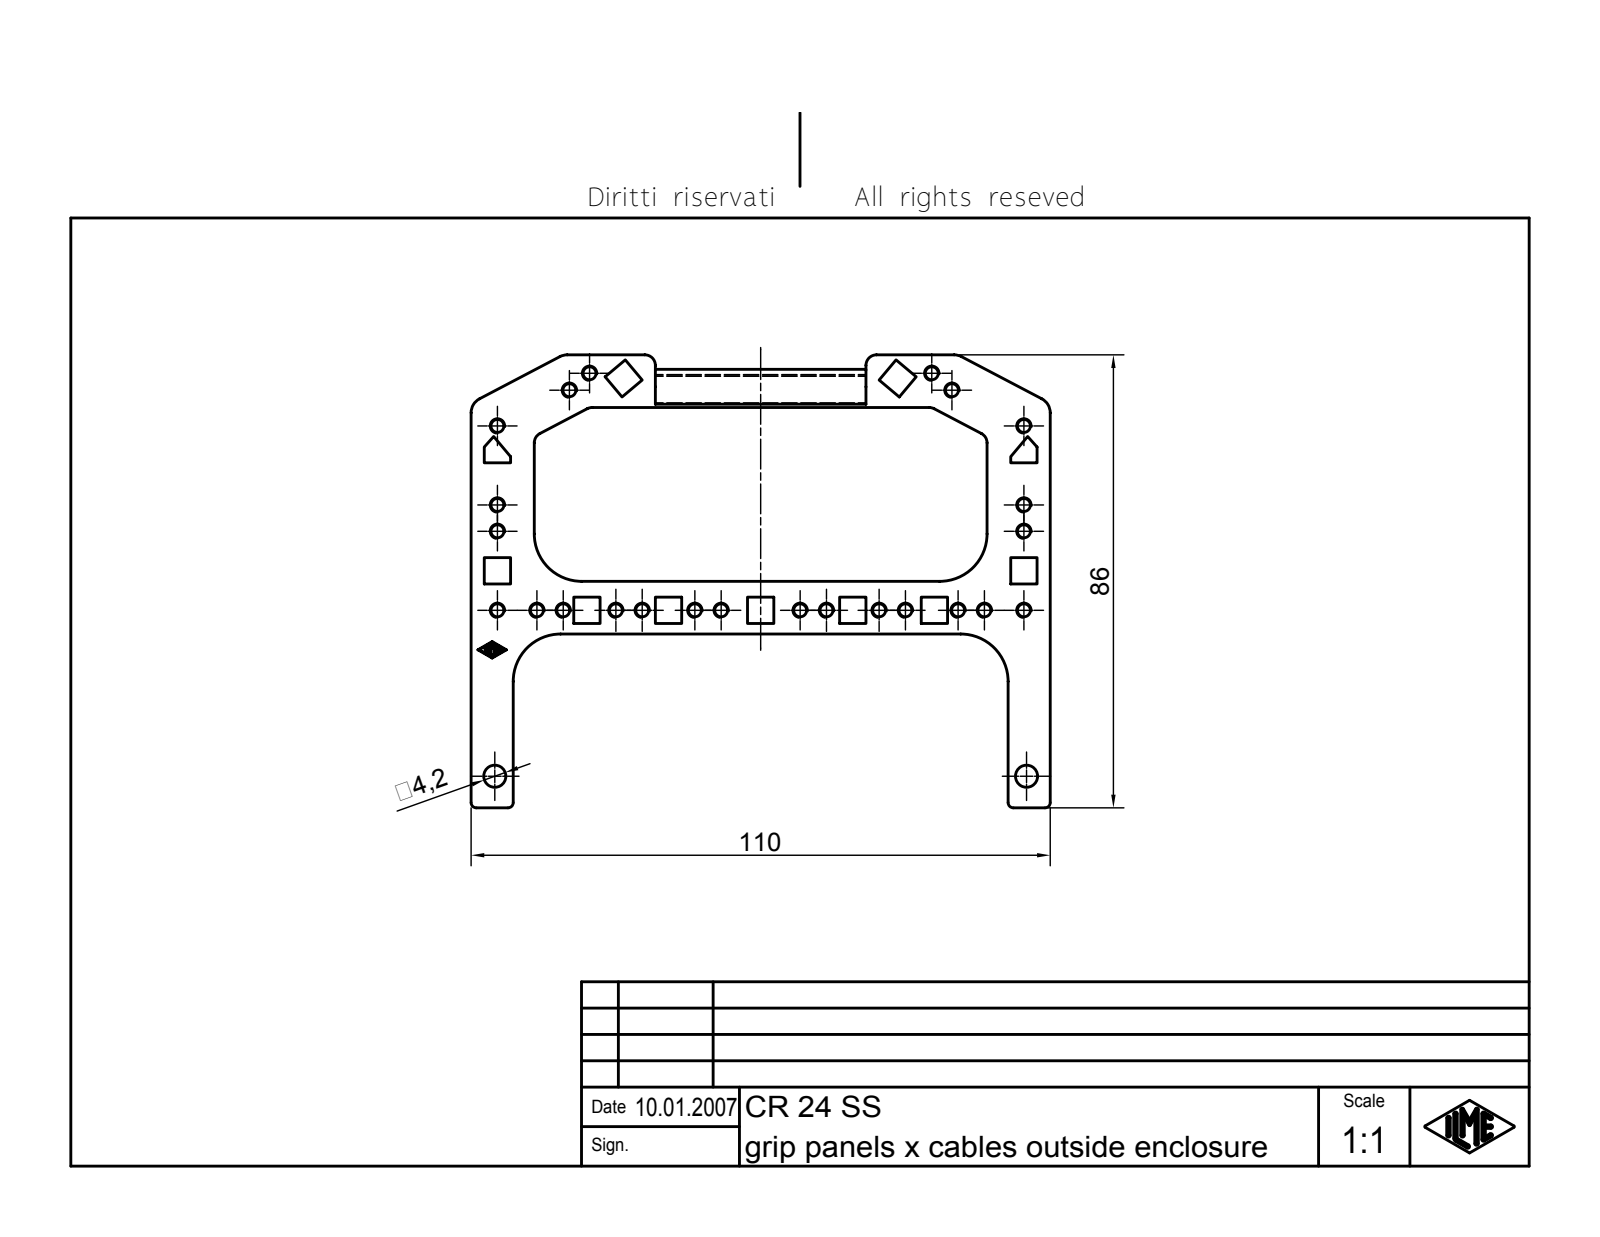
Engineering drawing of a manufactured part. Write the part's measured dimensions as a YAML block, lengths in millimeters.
part_name: "CR 24 SS"
step_written_by: "Autodesk Inventor 7 (AUTOMOTIVE_DESIGN)"
units: millimeters
bodies: {solids: 1, faces: 211, planar: 117, cylindrical: 46, other: 48}
overall_size: [110, 86, 5.5]
volume: 6434
surface_area: 9288
round_holes:
  - {diameter: 4.2, count: 2}
partial_cylinders:
  - {radius: 0.1, count: 14}
  - {radius: 2, count: 6}
  - {radius: 1, count: 4}
  - {radius: 3, count: 4}
  - {radius: 9, count: 4}
  - {radius: 1.75, count: 1}
  - {radius: 2.75, count: 1}
face_to_face_distances: [2, 1, 43, 10, 33, 5, 110, 8, 4, 35]
hole_center_spacings: [101]
